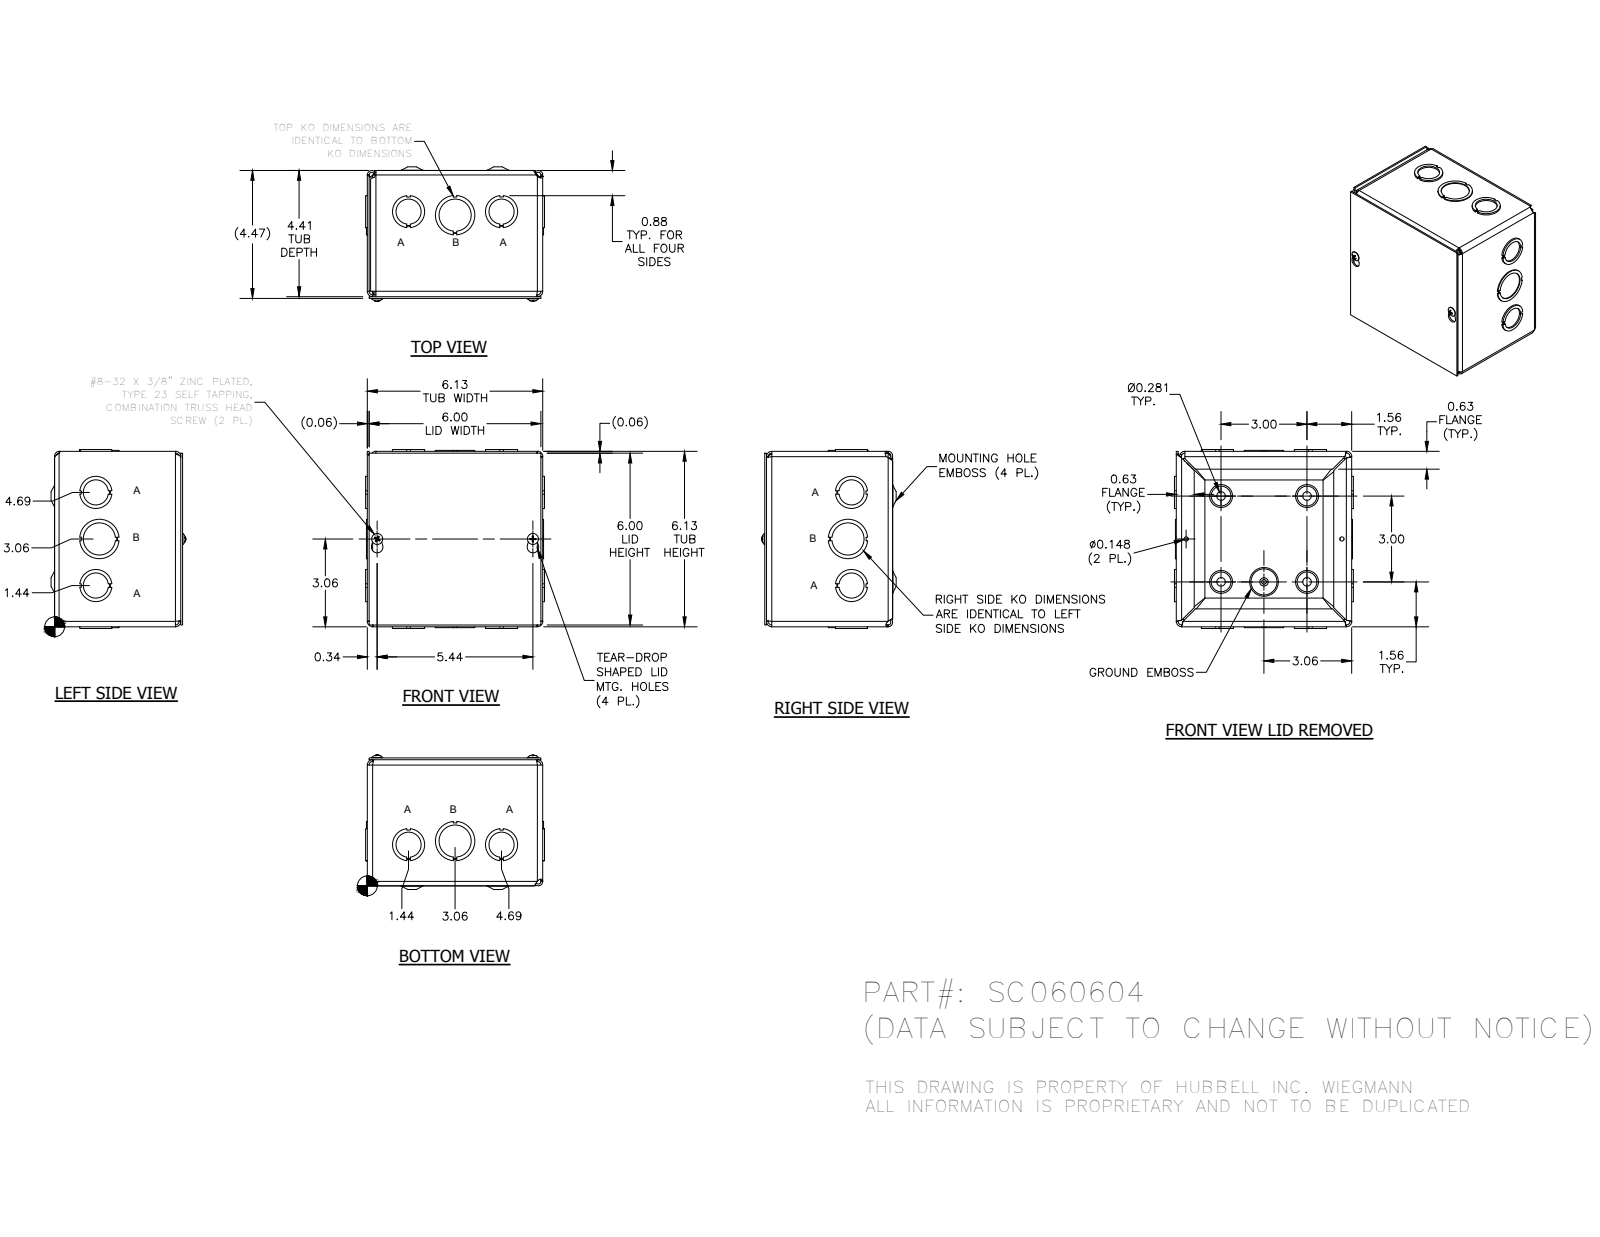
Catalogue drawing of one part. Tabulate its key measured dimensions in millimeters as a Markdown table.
| quantity | value |
| --- | --- |
| part name | SC0606BKP; SC060604WRA; SC0606LID; 34056 (+1 more) |
| STEP written by | Autodesk Inventor 2014 (AUTOMOTIVE_DESIGN) |
| units | millimeters |
| bodies | 20 solids, 630 faces (373 planar, 129 cylindrical, 128 other) |
| overall size | 158.72 × 158.72 × 119.2 |
| round holes (diameter × count) | 28.57 × 6, 7.62 × 4, 22.22 × 4, 3.76 × 2, 34.92 × 2, 4.19 × 1 |
| round bosses / shafts (diameter × count) | 9.75 × 2, 4.17 × 2, 5.8 × 1 |
| partial cylindrical surfaces (radius × count) | 3.17 × 10, 4.75 × 8, 1.4 × 4, 1.57 × 4, 2.38 × 4, 2.97 × 4, 3.15 × 4, 3.96 × 4 |
| main face-to-face distances | 1.57, 154, 110.32, 152.43, 111.89, 1.58, 1.59, 111.91, 113.48, 155.57 |
| hole center spacings | 49.09, 76.2, 38.1, 41.39, 41.4, 82.55, 85.19, 107.76 |
